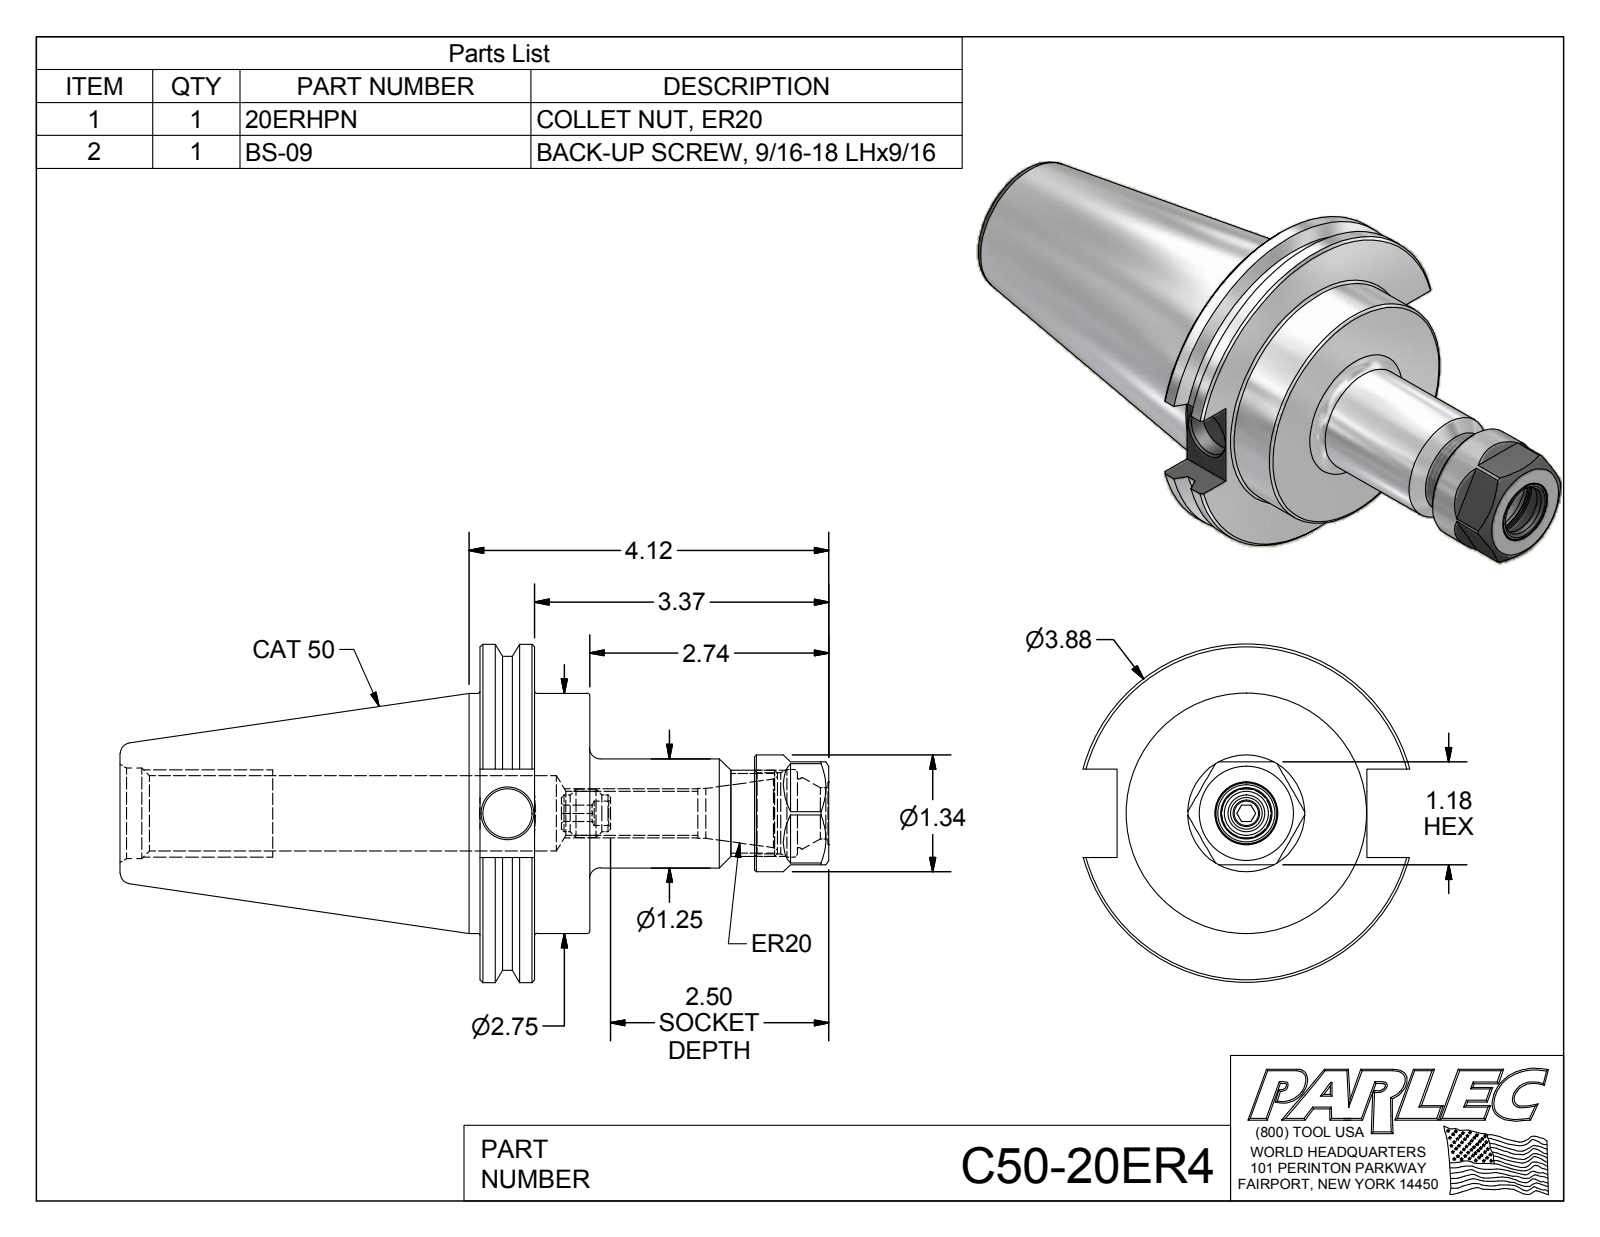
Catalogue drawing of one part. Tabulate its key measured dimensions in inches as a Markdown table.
| quantity | value |
| --- | --- |
| part name | C50-20ER4; C50-20ER4-1; 20ERHPN; BS-09 |
| STEP written by | Autodesk Inventor 2012 (AUTOMOTIVE_DESIGN) |
| units | inches |
| bodies | 3 solids, 107 faces (42 planar, 24 cylindrical, 41 other) |
| overall size | 8.12 × 3.875 × 3.74 |
| volume | 25.36 in³ |
| surface area | 94.92 in² |
| round holes (diameter × count) | 0.281 × 1, 0.502 × 1, 0.563 × 1, 0.57 × 1, 0.587 × 1, 0.79 × 1, 0.865 × 1, 0.926 × 1, 1.005 × 1, 1.038 × 1 |
| round bosses / shafts (diameter × count) | 3.875 × 1, 3.594 × 1, 2.75 × 1, 1.34 × 1, 1.25 × 1, 0.984 × 1, 0.555 × 1, 0.422 × 1 |
| main face-to-face distances | 0.625, 1.255, 0.63, 1.18, 3.145, 2.52, 1.89, 3.995, 3.37, 2.74 |
